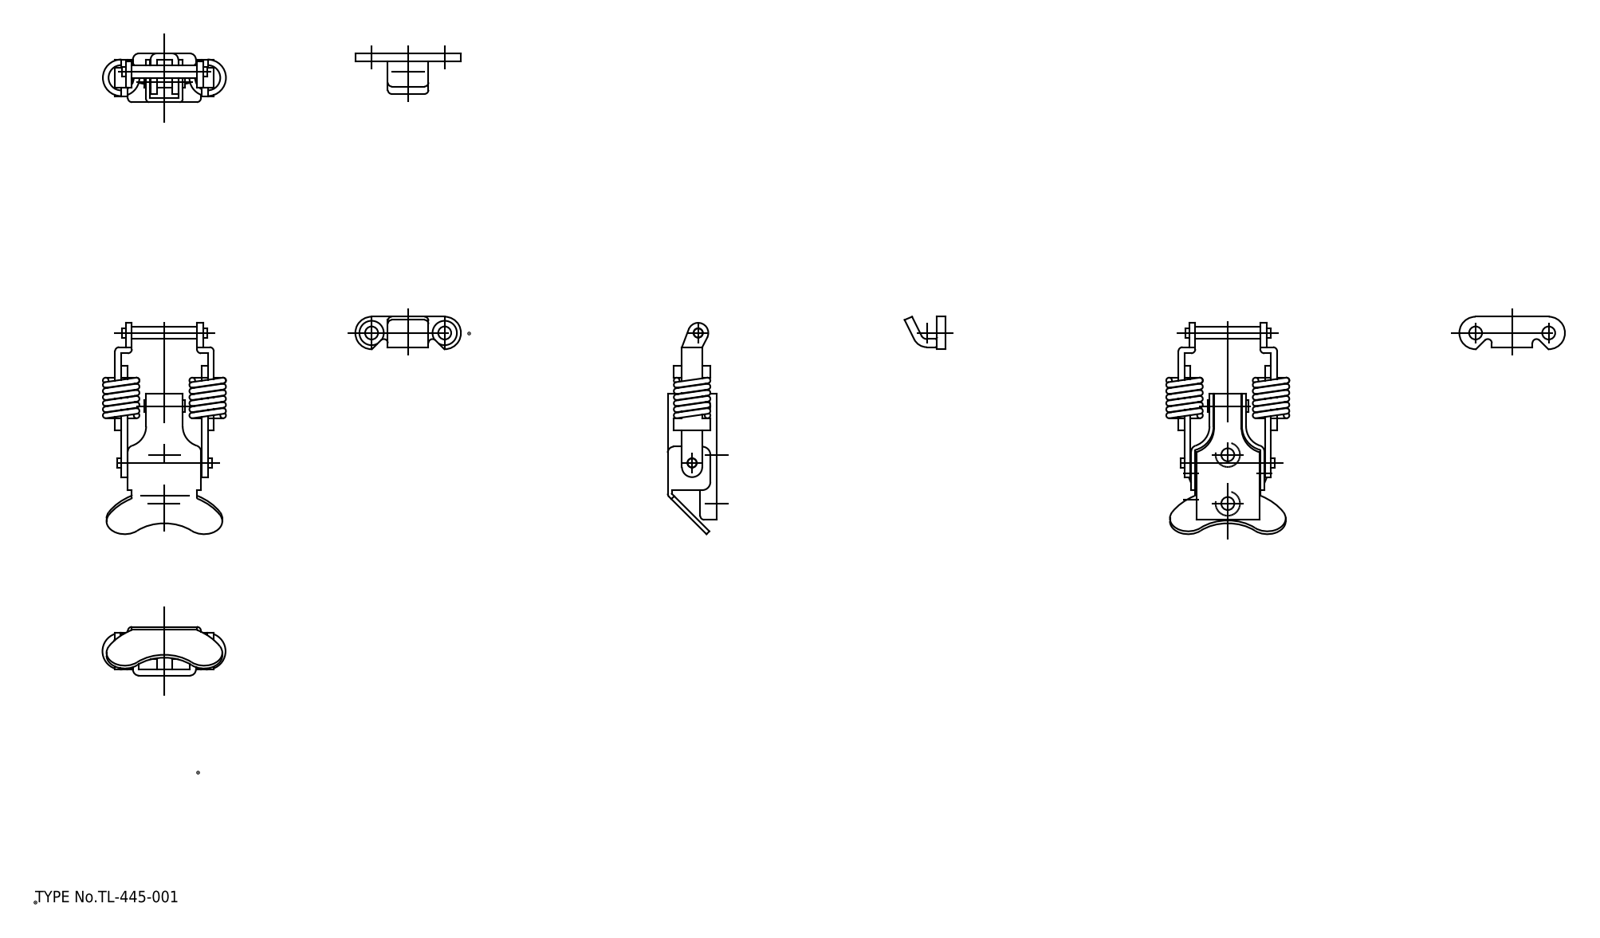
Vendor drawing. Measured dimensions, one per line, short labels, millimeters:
name: spring_mr; spring; shaft_C; shaft_B (+7 more)
written by: spGate 19.8.4 (****-****-****-****) (AUTOMOTIVE_DESIGN)
unit: mm
bodies: 12 solids, 403 faces (117 planar, 100 cylindrical, 186 other)
size: 53.54 × 30.3 × 12
volume: 3 965 mm³; area: 7 775 mm²
holes: 4× ⌀3.2, 2× ⌀2.3, 2× ⌀3.1
bosses: 3× ⌀3, 2× ⌀2.25
rounds: 9× R1, 8× R1.5, 5× R3, 4× R2, 3× R0.5, 2× R2.5, 2× R4, 2× R4.5
face distances: 1.5, 1, 21.3, 3.5, 4.5, 19.8, 3, 2, 7, 12
hole spacings: 12, 14.04, 18, 18.17, 31.29, 31.35, 32.04, 42.93
